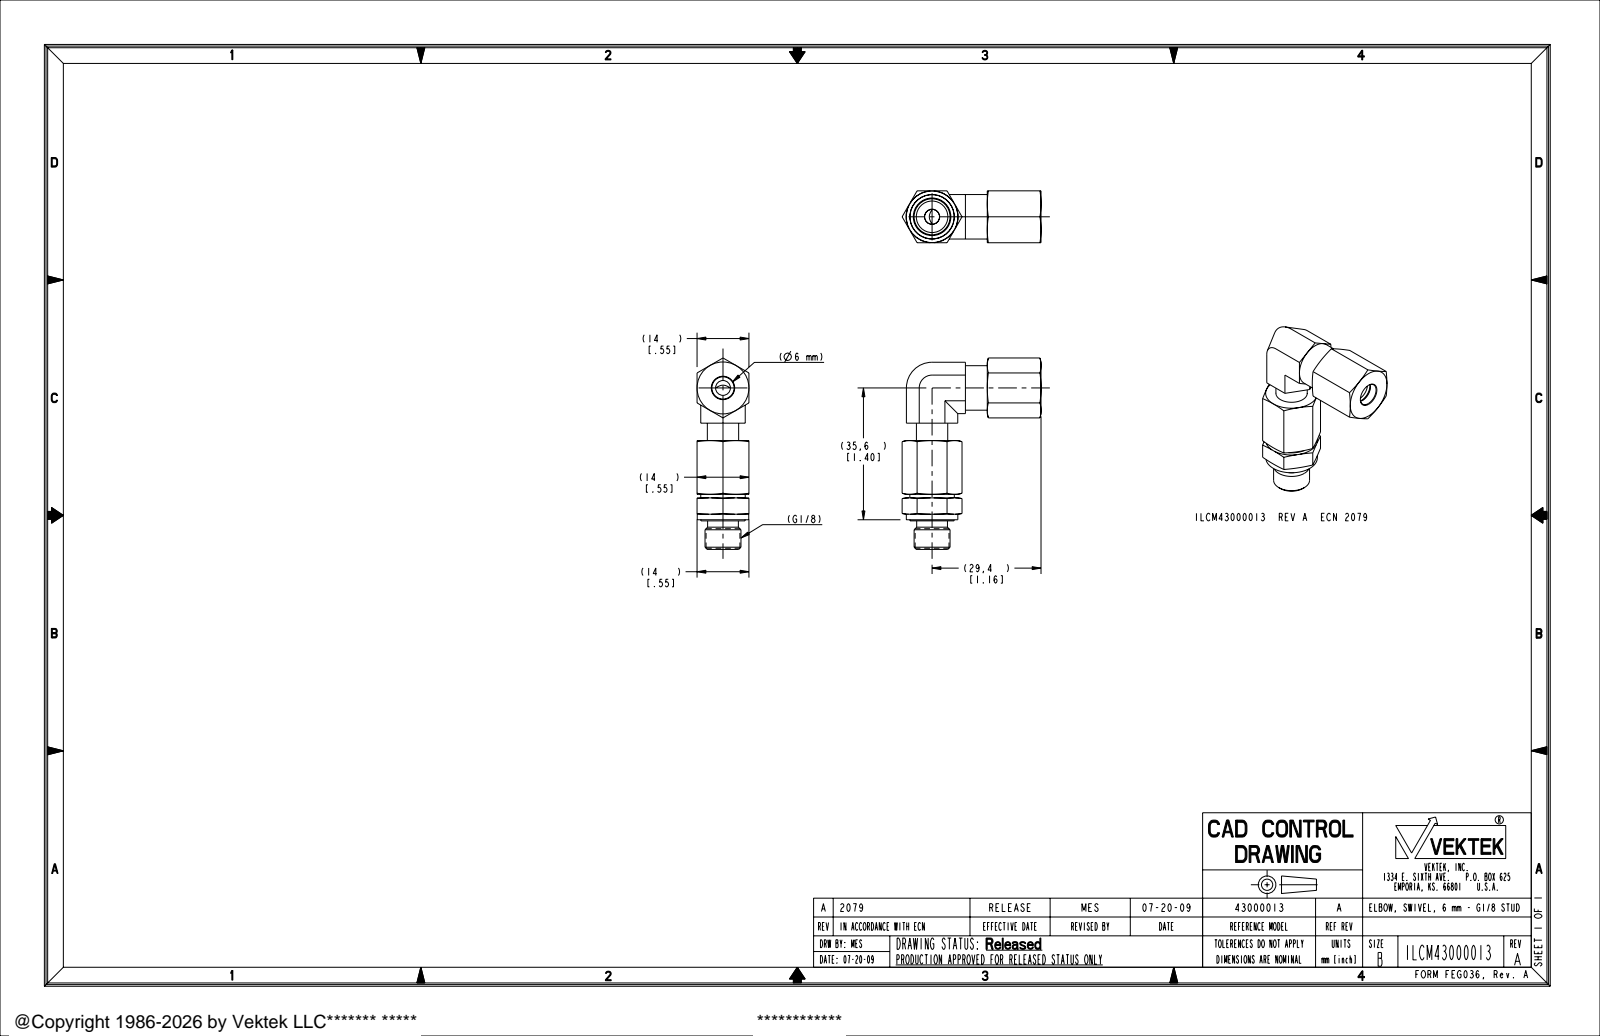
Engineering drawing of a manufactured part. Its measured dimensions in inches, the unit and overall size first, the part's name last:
Units: inches
Overall size (bounding box): 2.033 × 1.476 × 0.551
Round holes (diameter × count): ⌀0.157 ×2, ⌀0.236 ×2, ⌀0.409 ×2, ⌀0.331 ×1, ⌀0.333 ×1, ⌀0.472 ×1
Round bosses / shafts (diameter × count): ⌀0.547 ×1, ⌀0.472 ×1, ⌀0.469 ×1, ⌀0.382 ×1, ⌀0.374 ×1, ⌀0.36 ×1, ⌀0.333 ×1, ⌀0.327 ×1
Main face-to-face distances: 0.551, 0.039, 0.512, 0.472, 0.571, 0.185, 0.232, 1.156, 1.341, 0.547
Volume: 0.5 in³ · Surface area: 9.322 in²
Bodies: 1 solid, 185 faces (57 planar, 46 cylindrical, 82 other)
Part name (STEP PRODUCT): ILCM43000013
STEP written by: PRO/ENGINEER BY PARAMETRIC TECHNOLOGY CORPORATION, 2007460 (AUTOMOTIVE_DESIGN_CC2)
